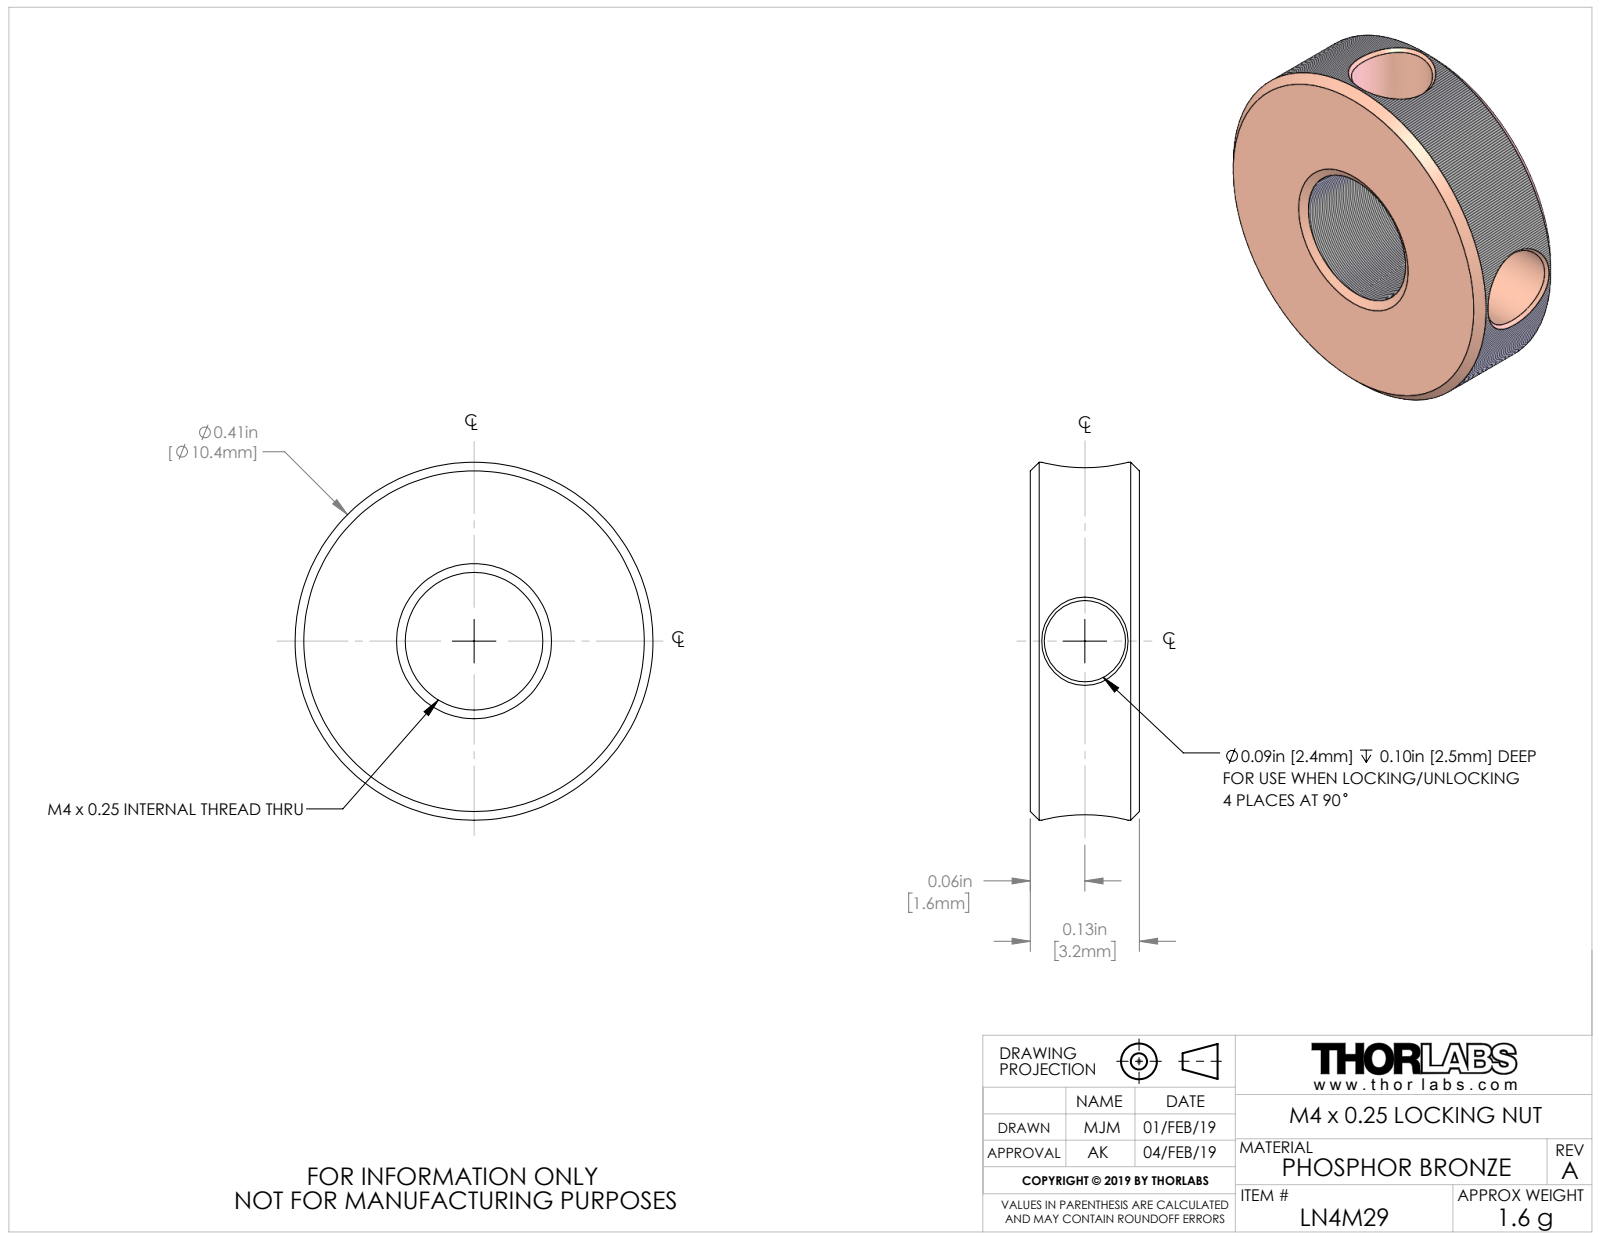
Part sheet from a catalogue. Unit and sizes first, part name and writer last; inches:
Units: inches
Overall size (bounding box): 0.41 × 0.41 × 0.125
Round holes (diameter × count): ⌀0.093 ×2, ⌀0.157 ×1
Round bosses / shafts (diameter × count): ⌀0.41 ×1
Main face-to-face distances: 0.125, 0.19
Volume: 0.011 in³ · Surface area: 0.551 in²
Bodies: 1 solid, 34 faces (6 planar, 12 cylindrical, 16 other)
Part name (STEP PRODUCT): TTN174841-E0W
STEP written by: SolidWorks 2018 (AUTOMOTIVE_DESIGN)
